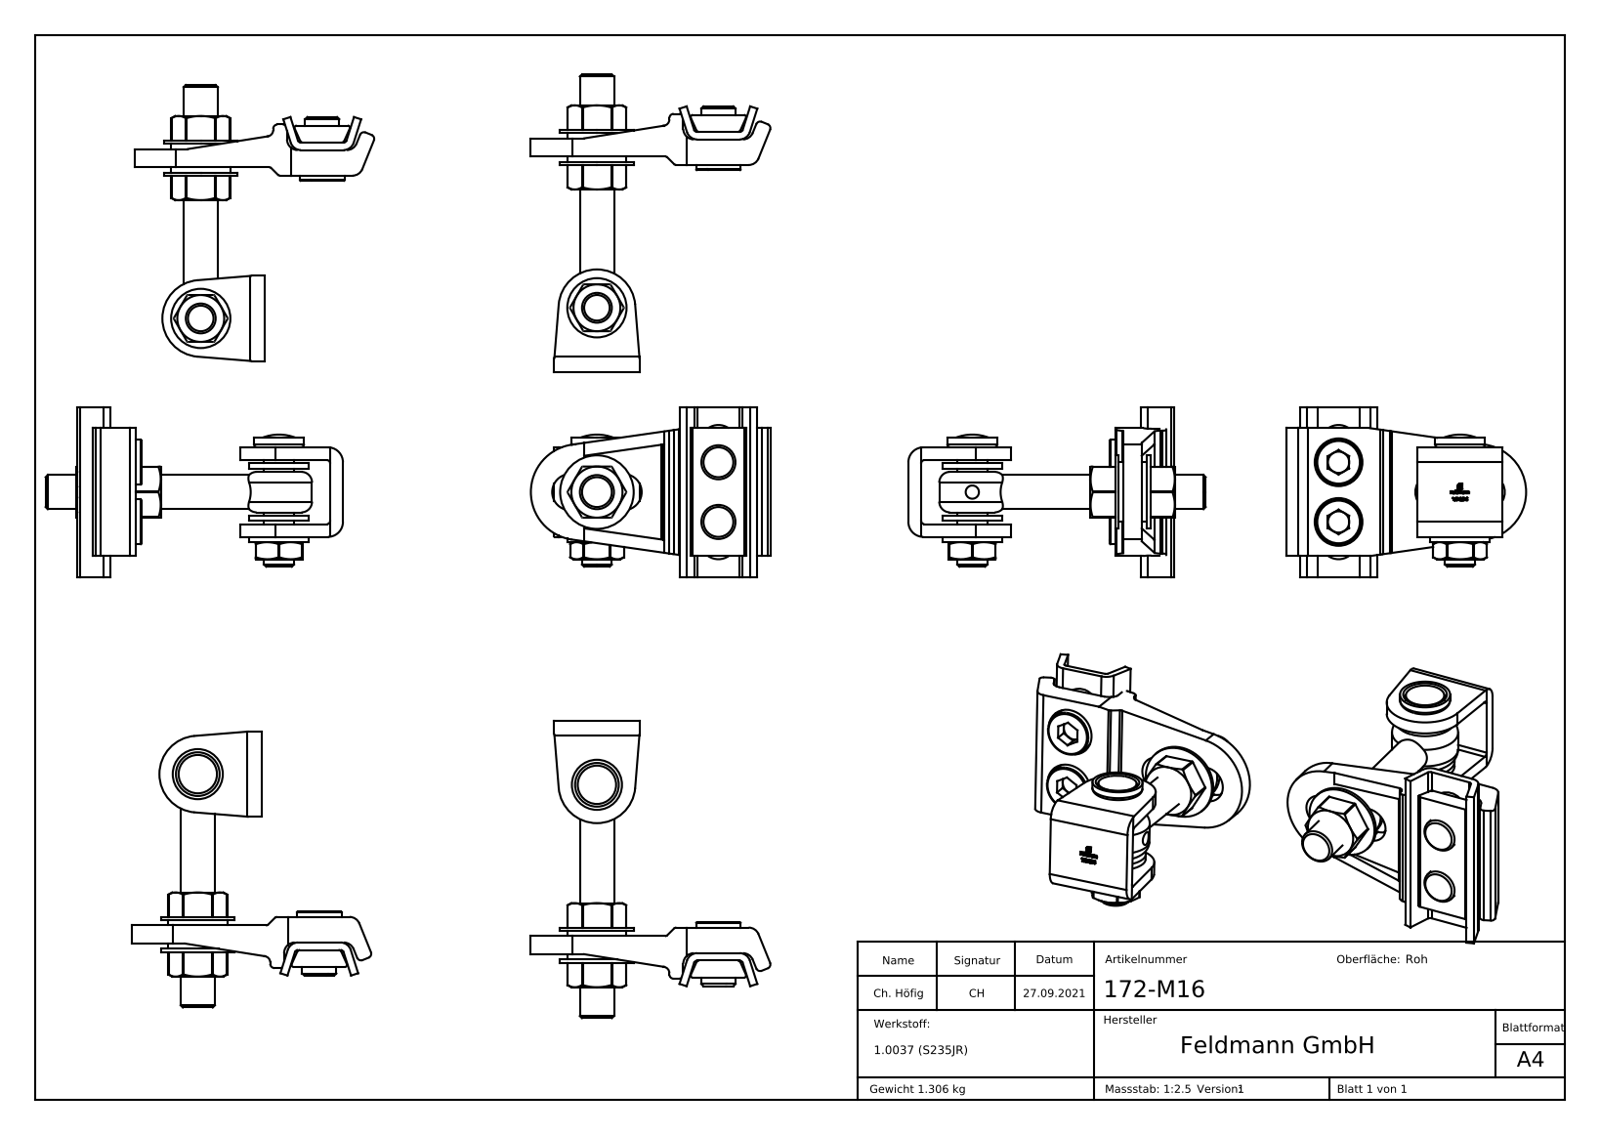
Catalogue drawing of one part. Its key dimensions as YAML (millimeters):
part_name: "172-M16; 172-Mxx Teil4_172-M16 Teil4; DIN 1661 M4-M20_DIN 1661 M16; 172-Mxx Teil7_172-M16 Teil7 (+8 more)"
step_written_by: "SolidWorks 2018 (CONFIG_CONTROL_DESIGN)"
units: millimeters
bodies: {solids: 17, faces: 488, planar: 268, cylindrical: 85, other: 135}
overall_size: [139.5, 112.4, 80]
volume: 167210
surface_area: 69987
round_holes:
  - {diameter: 14, count: 3}
  - {diameter: 6.2, count: 2}
  - {diameter: 15.2, count: 2}
  - {diameter: 19, count: 2}
  - {diameter: 22.4, count: 2}
  - {diameter: 12, count: 1}
  - {diameter: 14.5, count: 1}
  - {diameter: 15, count: 1}
  - {diameter: 20.5, count: 1}
round_bosses_or_shafts:
  - {diameter: 16, count: 3}
  - {diameter: 27.8, count: 2}
  - {diameter: 21, count: 2}
  - {diameter: 34.5, count: 1}
  - {diameter: 31, count: 1}
  - {diameter: 23.5, count: 1}
  - {diameter: 18, count: 1}
  - {diameter: 14.2, count: 1}
partial_cylinders:
  - {radius: 0.5, count: 12}
  - {radius: 1.5, count: 8}
  - {radius: 5, count: 5}
  - {radius: 2, count: 4}
  - {radius: 8.5, count: 4}
  - {radius: 1, count: 2}
  - {radius: 7, count: 2}
  - {radius: 3, count: 1}
face_to_face_distances: [2.5, 8.5, 15, 4, 11.5, 3.5, 11, 1.5, 6, 12.5]
hole_center_spacings: [58.69, 28]
